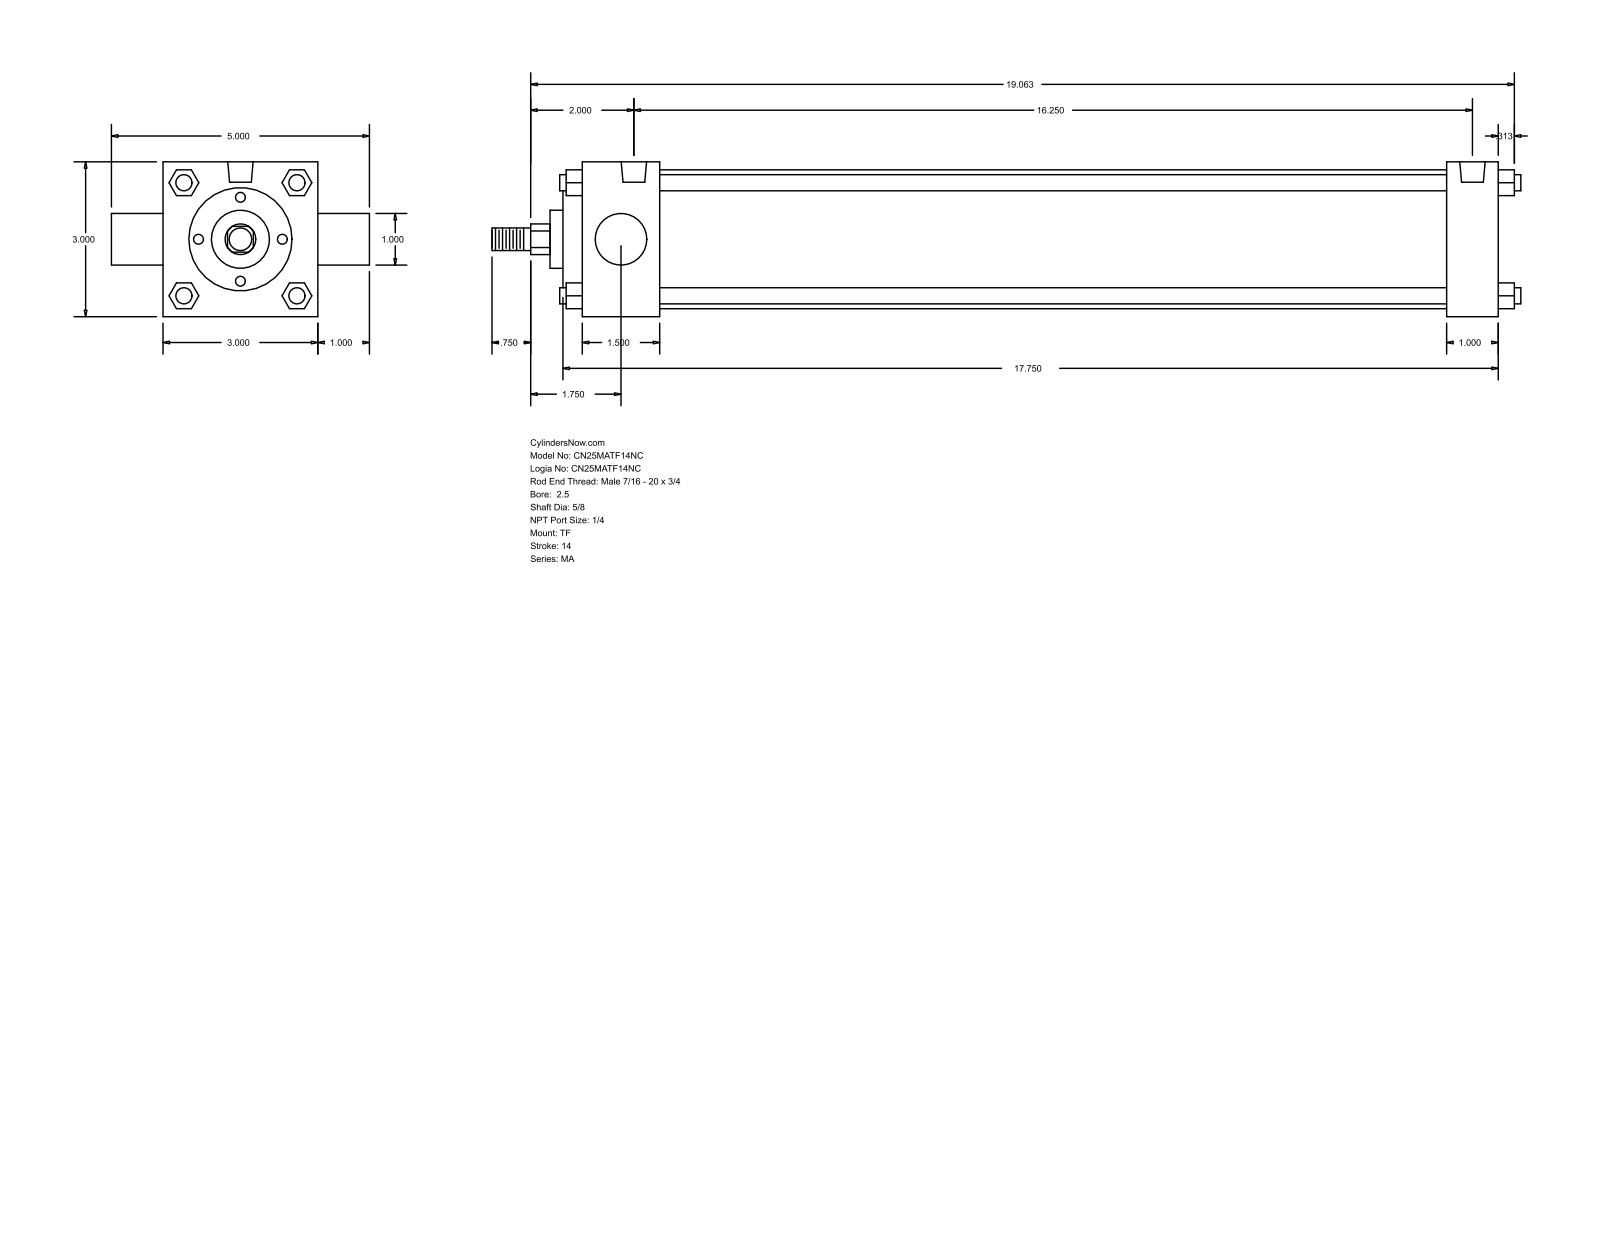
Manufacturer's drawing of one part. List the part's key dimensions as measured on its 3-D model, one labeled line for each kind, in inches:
Part name (STEP PRODUCT): MA_TF__0250_0.625
STEP written by: GSSL Pune (CONFIG_CONTROL_DESIGN)
Units: inches
Bodies: 0 solids, 122 faces (93 planar, 29 cylindrical, 0 other)
Overall size (bounding box): 19.937 × 5 × 3
Round holes (diameter × count): ⌀0.313 ×3, ⌀0.492 ×2
Round bosses / shafts (diameter × count): ⌀0.313 ×4, ⌀2.69 ×1, ⌀2 ×1, ⌀1.125 ×1, ⌀1 ×1, ⌀0.625 ×1, ⌀0.437 ×1
Partial cylindrical surfaces — rounded edges, fillets, slot ends (radius × count): R0.297 ×1
Main face-to-face distances: 3, 17.75, 1, 1.5, 16.75, 15.25, 16.25, 0.5, 0.375, 1.875
Hole centre spacings: 16.25
